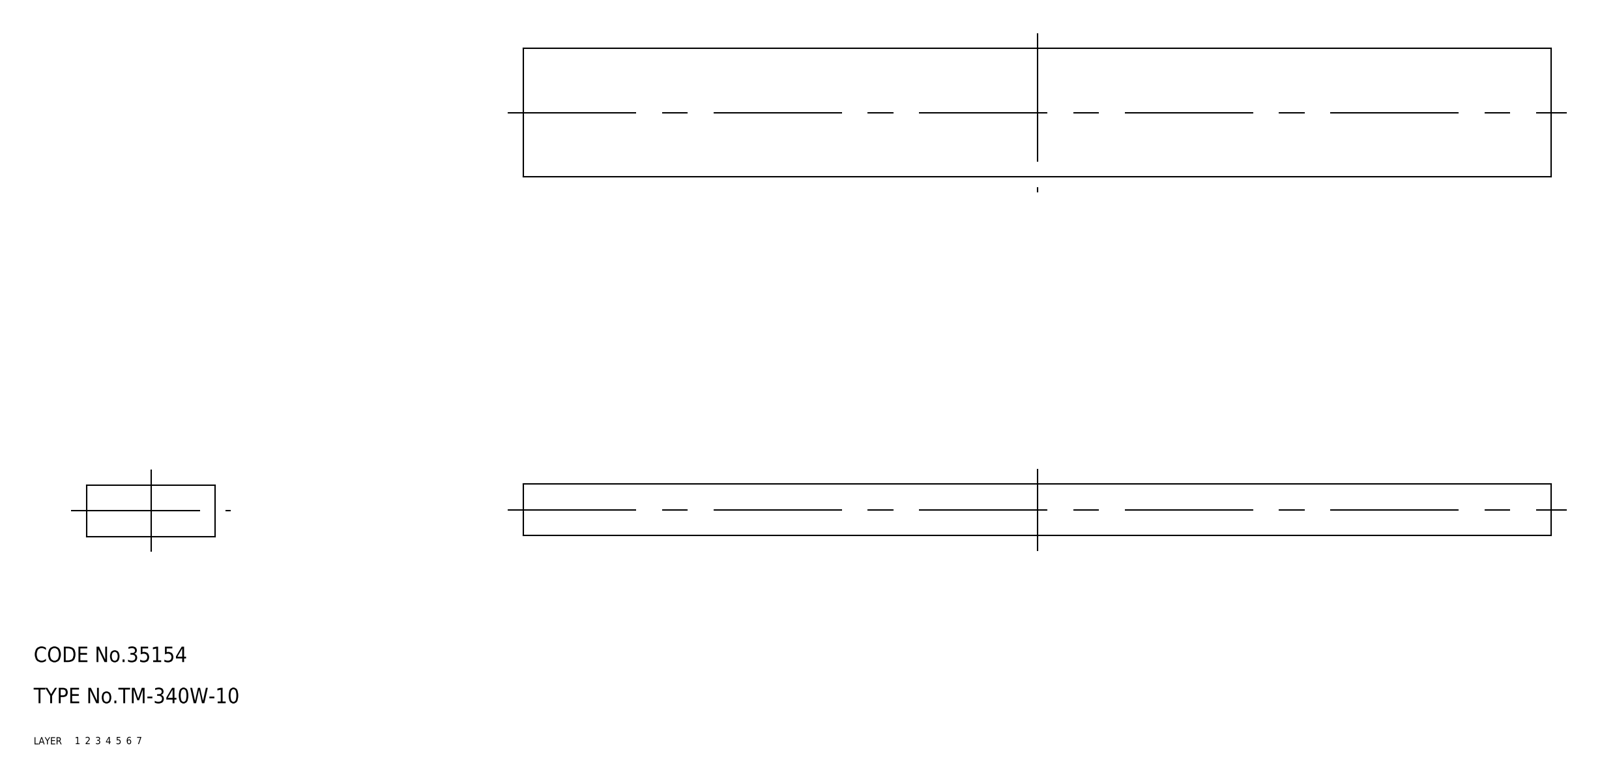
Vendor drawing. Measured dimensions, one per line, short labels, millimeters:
name: TM_340W_10; rubber foam
written by: SolidWorks 2015 (AUTOMOTIVE_DESIGN)
unit: mm
bodies: 1 solid, 6 faces (6 planar, 0 cylindrical, 0 other)
size: 200 × 25 × 10
volume: 50 000 mm³; area: 14 500 mm²
face distances: 10, 25, 200
